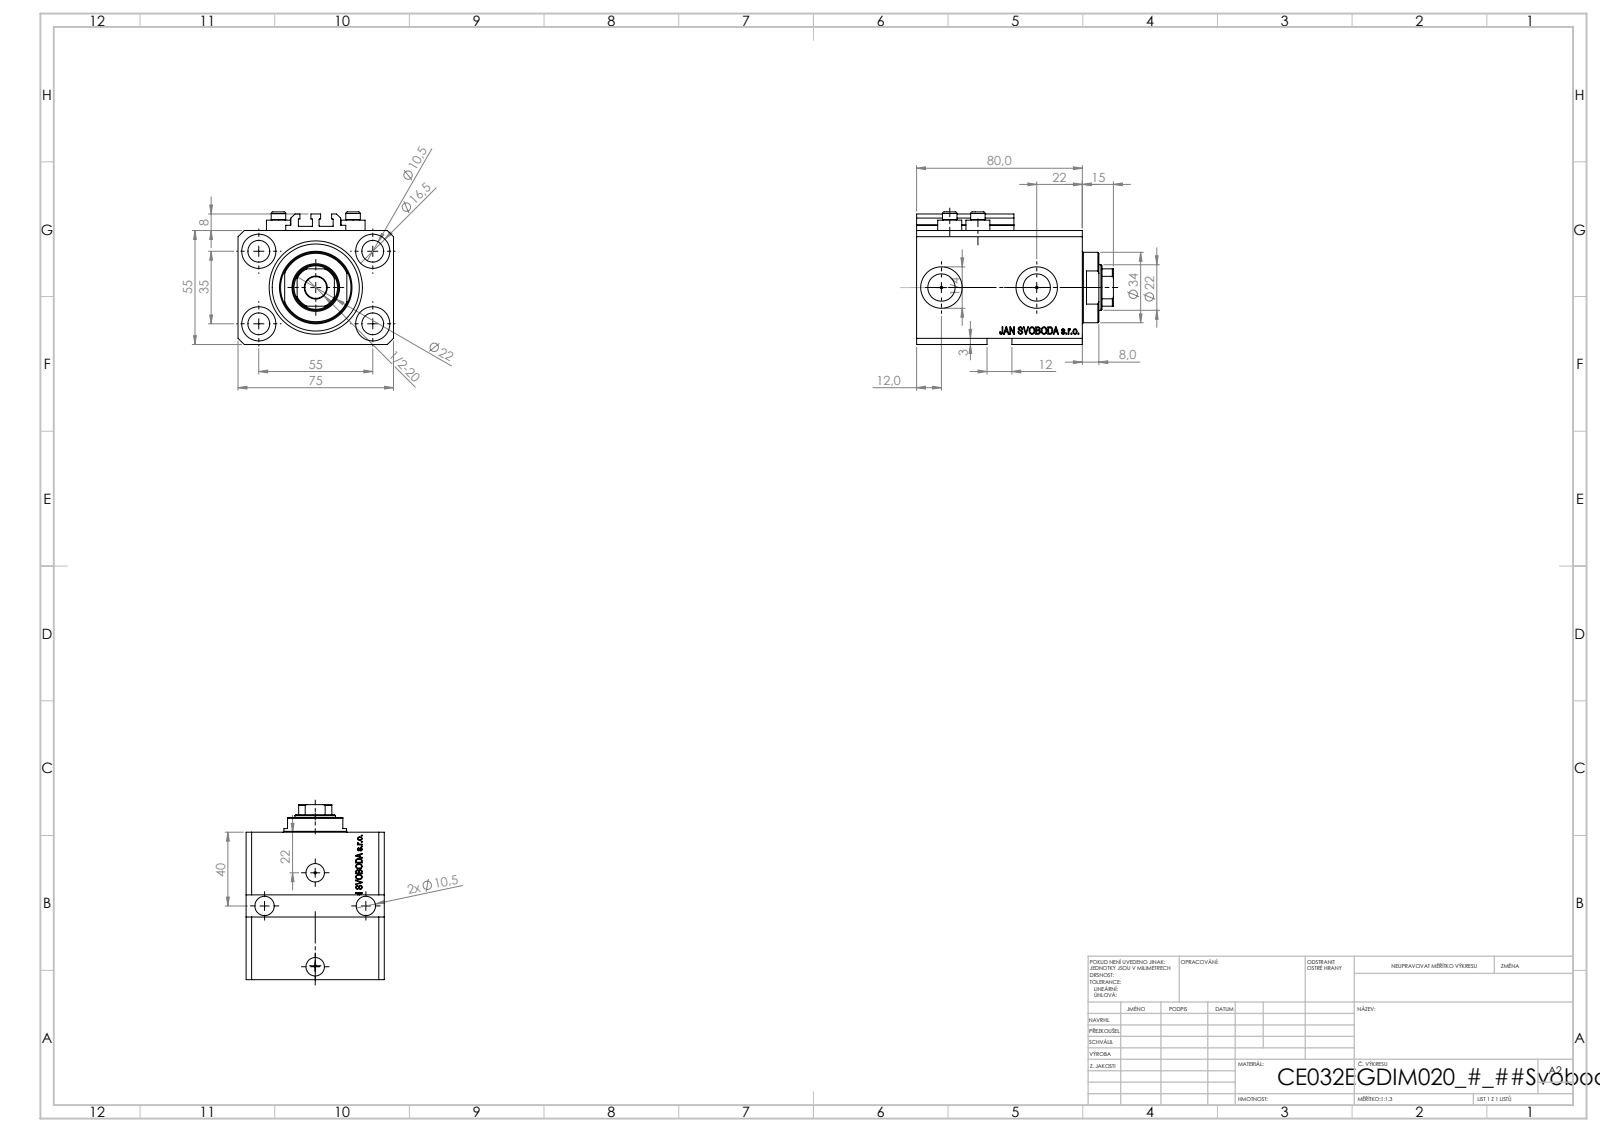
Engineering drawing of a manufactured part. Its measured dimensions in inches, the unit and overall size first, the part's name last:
Units: inches
Overall size (bounding box): 3.74 × 2.953 × 2.52
Round holes (diameter × count): ⌀0.413 ×7, ⌀0.049 ×4, ⌀0.157 ×4, ⌀0.65 ×4, ⌀0.394 ×2, ⌀0.518 ×2, ⌀0.787 ×2, ⌀0.866 ×1, ⌀1.26 ×1, ⌀1.772 ×1
Round bosses / shafts (diameter × count): ⌀0.457 ×4, ⌀0.276 ×4, ⌀1.339 ×1
Partial cylindrical surfaces — rounded edges, fillets, slot ends (radius × count): R0.008 ×10, R0.413 ×1
Main face-to-face distances: 2.165, 2.953, 0.591, 3.15, 2.559, 0.118, 0.39, 2.169, 2.76, 2.126
Hole centre spacings: 1.283, 2.165, 0.535, 0.555, 0.783, 0.792, 1.016, 1.121
Volume: 17.1 in³ · Surface area: 117.2 in²
Bodies: 8 solids, 1080 faces (518 planar, 138 cylindrical, 424 other)
Part name (STEP PRODUCT): V250CE_E_Body; V250CE_VC_E; ALLEN BOLT V250CE; V250CE_C_VCP
STEP written by: SolidWorks 2019 (CONFIG_CONTROL_DESIGN)
